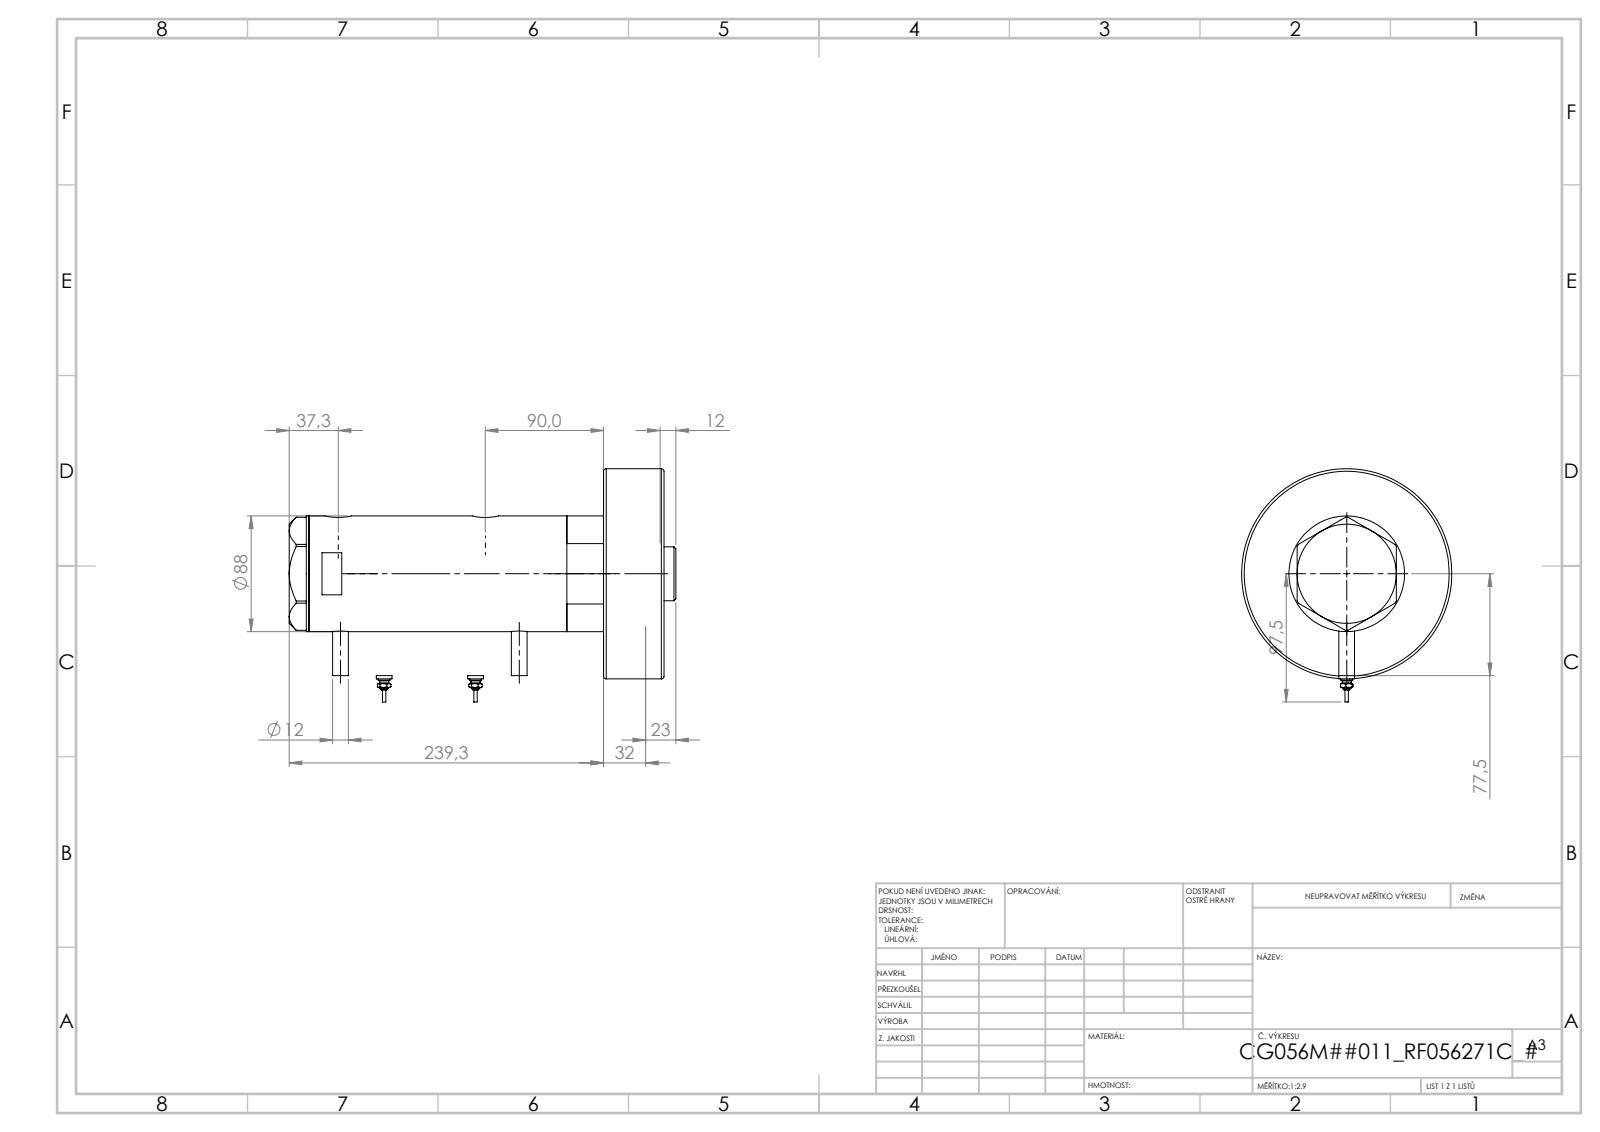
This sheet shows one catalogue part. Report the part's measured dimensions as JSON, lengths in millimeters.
{"part_name": "V270CG_BACK; V270CG_MIDDLE; V270CG_SWITCH; V270CG_FRONT (+2 more)", "step_written_by": "SolidWorks 2019 (CONFIG_CONTROL_DESIGN)", "units": "millimeters", "bodies": {"solids": 7, "faces": 242, "planar": 83, "cylindrical": 81, "other": 78}, "overall_size": [235.47, 160, 160], "volume_mm3": 1941000, "surface_area_mm2": 253105, "round_holes": [[5, 2], [12.5, 2], [13.16, 2], [20, 2], [14.5, 1], [42, 1], [43.5, 1], [56, 1], [60, 1], [75, 1], [80, 1]], "round_bosses_or_shafts": [[12, 2], [9, 2], [7, 2], [4.34, 2], [2.4, 2], [160, 1], [88, 1], [73, 1]], "face_to_face_distances": [46, 162.9, 208.9, 85.4, 77.5, 123.5, 26, 59.4, 136.9, 182.9], "hole_center_spacings": [1.7, 25.8, 61.3, 63, 87.1, 88.8]}
